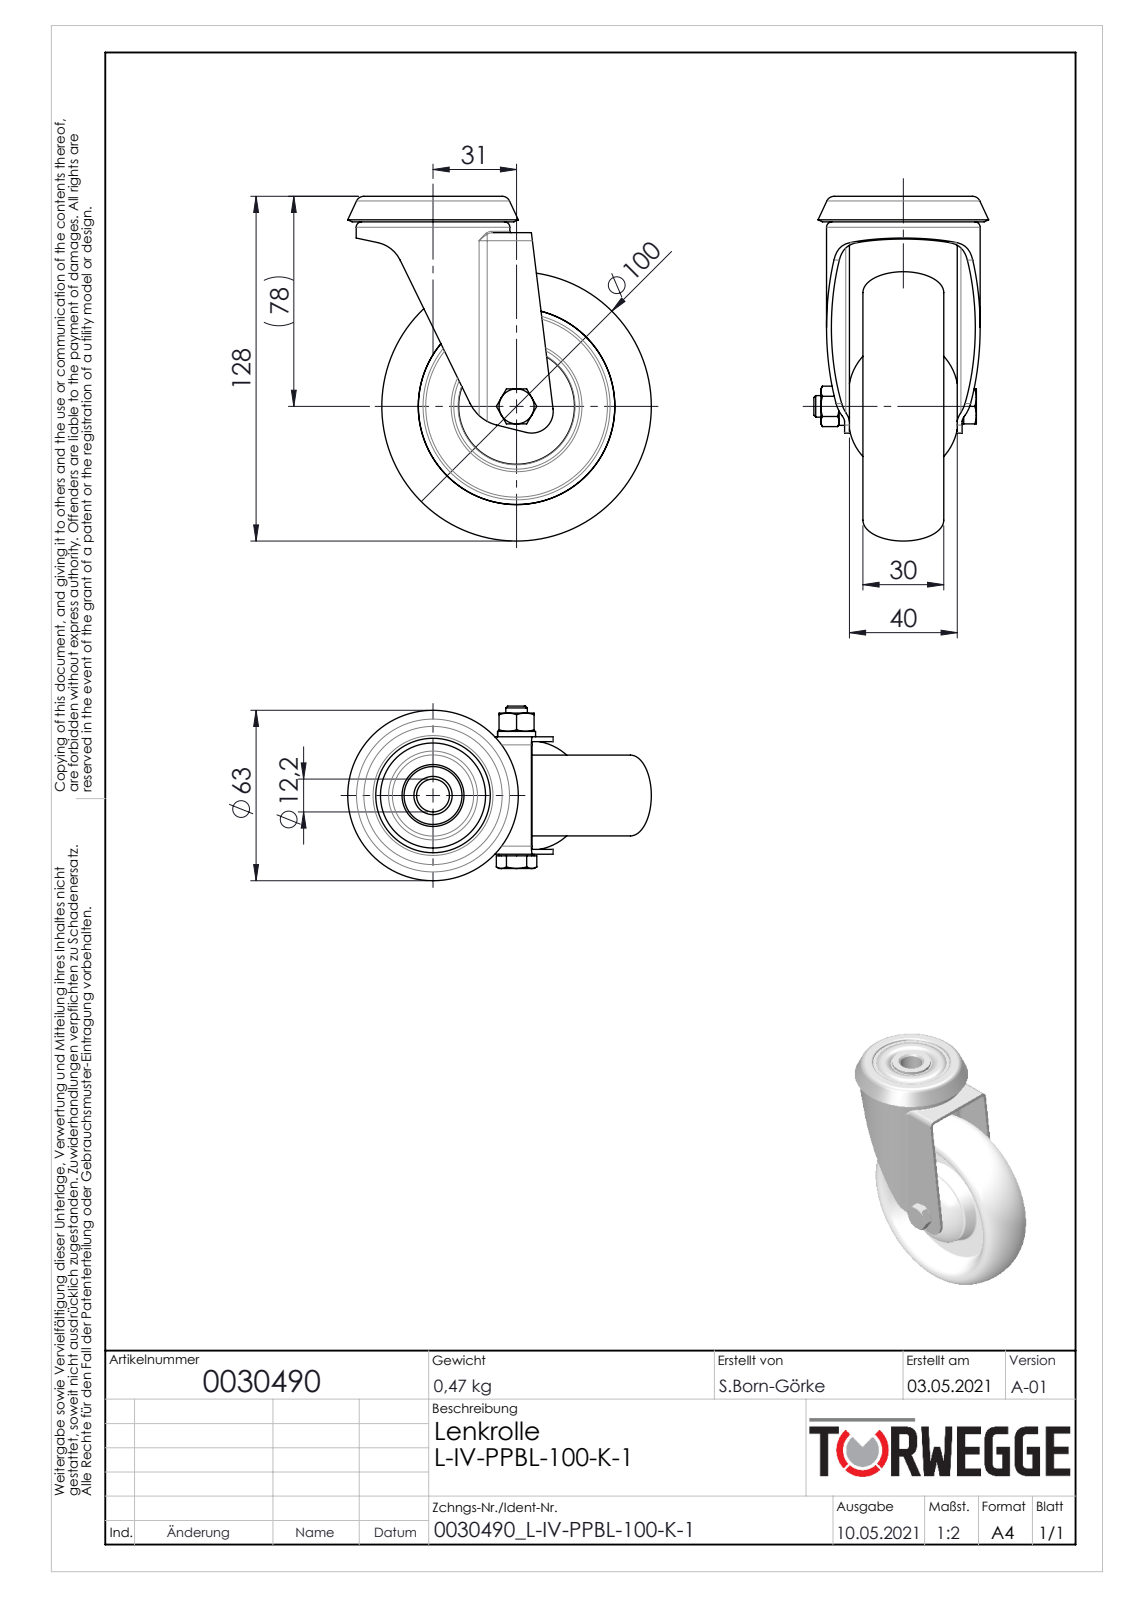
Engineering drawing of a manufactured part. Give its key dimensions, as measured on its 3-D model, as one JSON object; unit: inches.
{"part_name": "0030490", "step_written_by": "SolidWorks 2020 (AUTOMOTIVE_DESIGN)", "units": "inches", "bodies": {"solids": 9, "faces": 292, "planar": 70, "cylindrical": 74, "other": 148}, "overall_size": [5.039, 4.435, 2.553], "volume_in3": 12.22, "surface_area_in2": 137.8, "round_holes": [[0.268, 1], [0.315, 1], [0.319, 1], [0.327, 1], [0.48, 1], [1.142, 1], [1.299, 1], [1.378, 1], [2.102, 1]], "round_bosses_or_shafts": [[2.244, 1], [0.846, 1], [0.827, 1], [0.591, 1], [0.555, 1], [0.512, 1]], "partial_cylinders_radius": [[0.047, 2], [0.118, 2], [0.197, 2], [0.268, 2], [0.315, 1], [0.473, 1], [0.591, 1]], "face_to_face_distances": [0.071, 0.74, 0.669, 0.906, 0.976, 1.646, 0.374, 0.197, 0.445, 0.679]}
